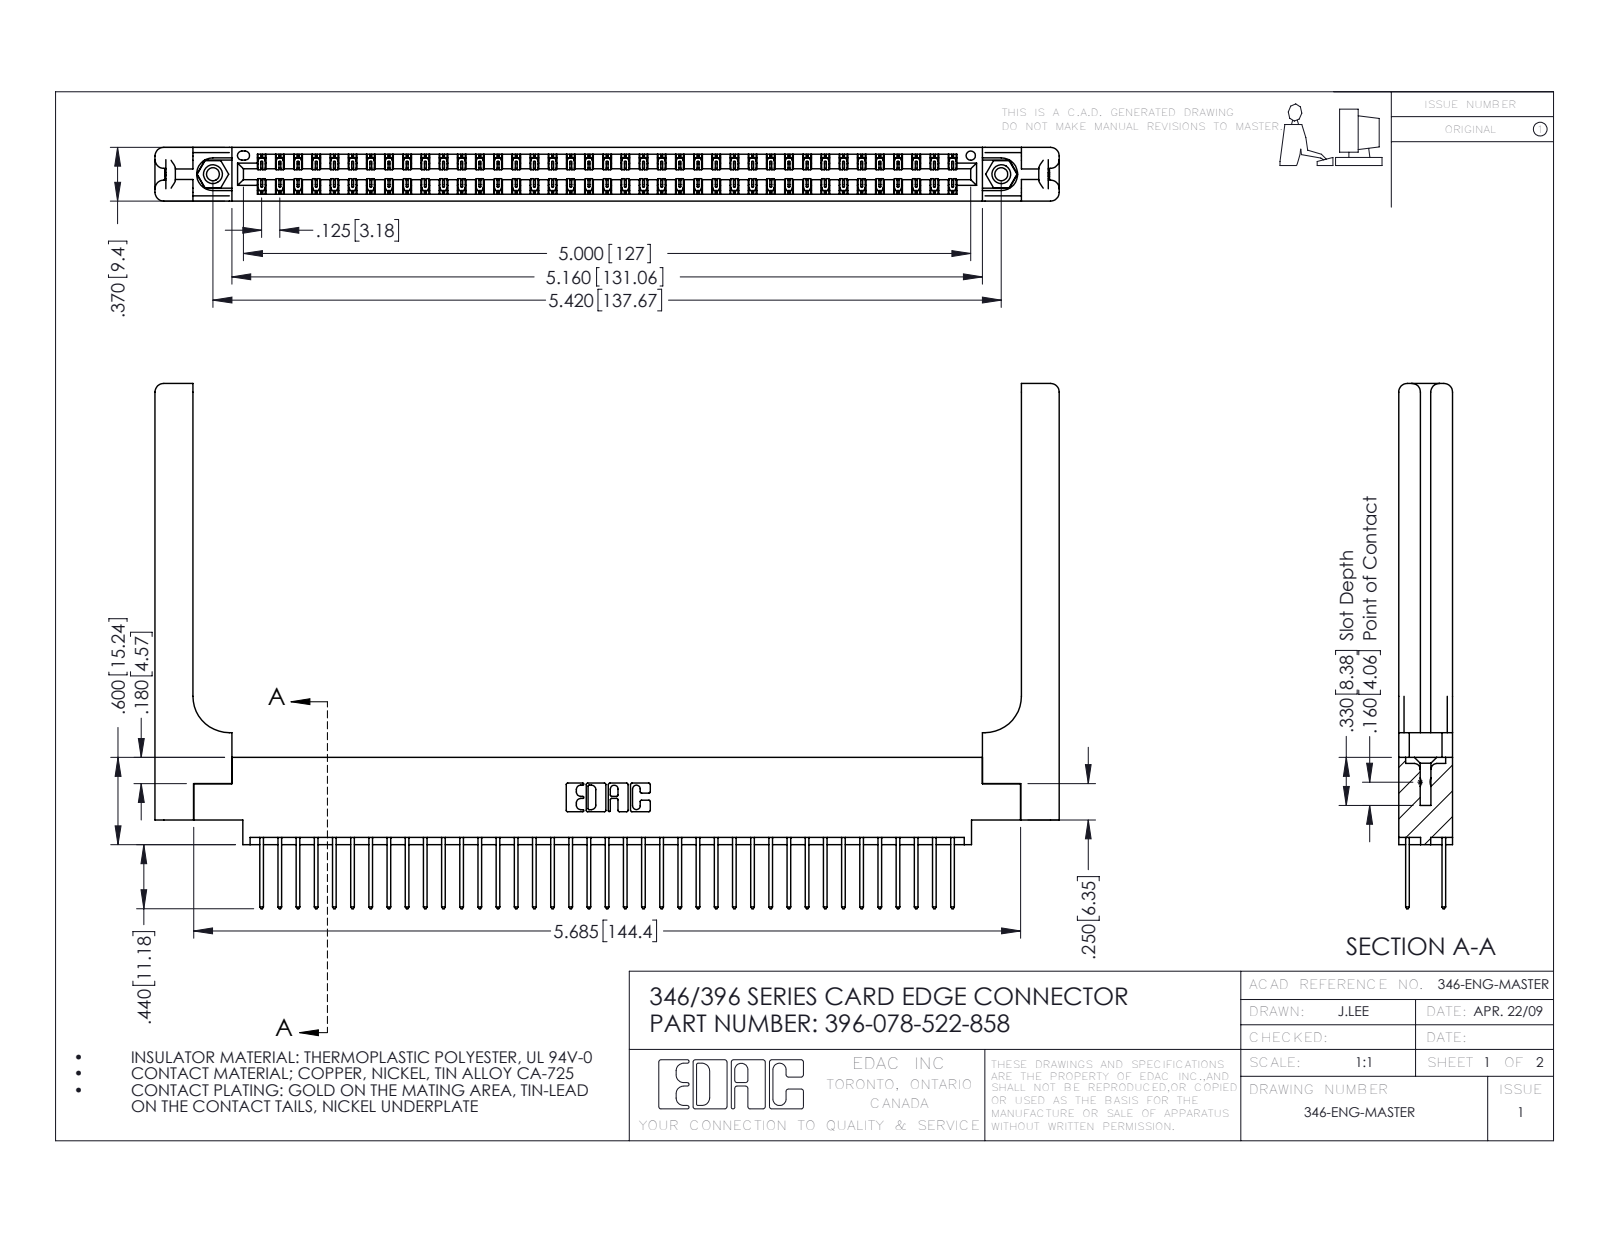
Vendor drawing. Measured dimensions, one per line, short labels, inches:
name: 346 Part_0.170 Offset - 0.156 Dia-TH; 345-292-001_345-293-122; 346-220-058_345-220-058; 396-078-522-858 (+1 more)
written by: SolidWorks 2016 (CONFIG_CONTROL_DESIGN)
unit: in
bodies: 83 solids, 4438 faces (2958 planar, 1420 cylindrical, 60 other)
size: 6.216 × 3.61 × 0.37
volume: 1.398 in³; area: 42.2 in²
holes: 2× ⌀0.089, 2× ⌀0.125, 2× ⌀0.156, 1× ⌀0.064
bosses: 2× ⌀0.155
rounds: 117× R0.006, 78× R0.01, 22× R0.01, 16× R0.06, 6× R0.007, 6× R0.031, 3× R0.026, 2× R0.014
face distances: 0.048, 0.322, 0.37, 0.072, 0.25, 0.025, 0.298, 0.148, 0.15, 0.275
hole spacings: 0.246, 5.211, 5.42
